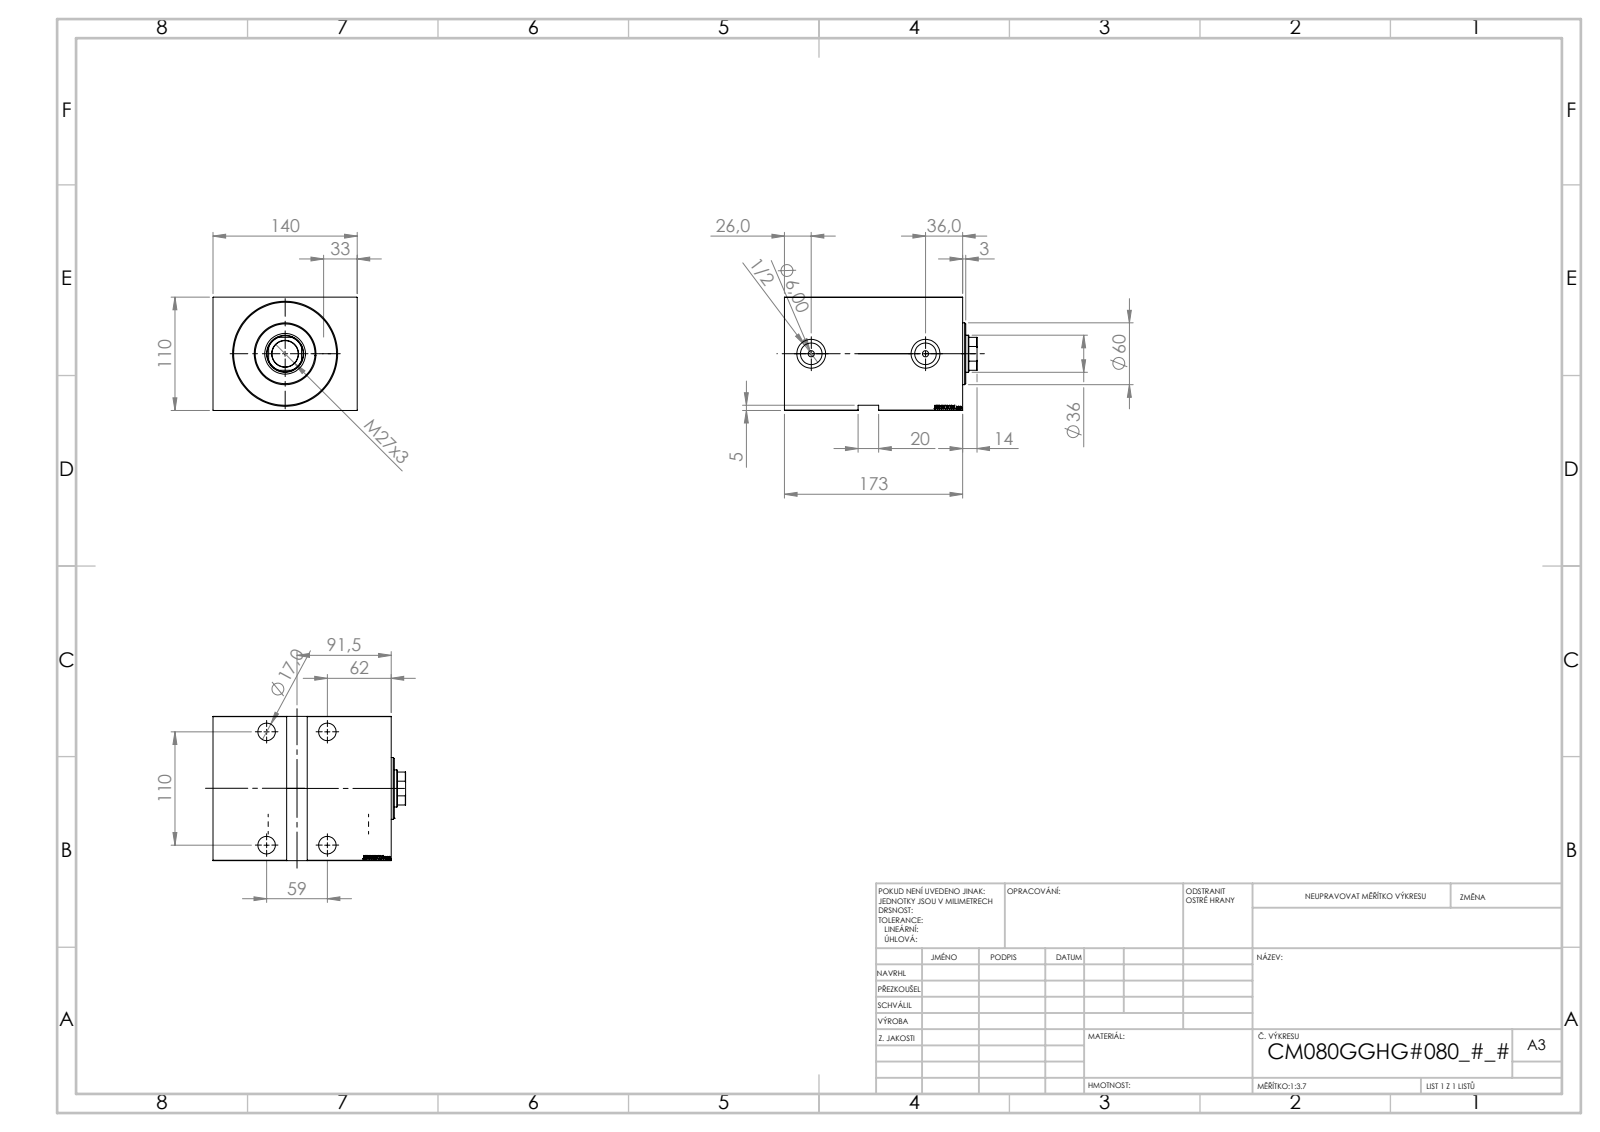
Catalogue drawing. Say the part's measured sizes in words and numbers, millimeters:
The part is named "V450CM_VC_G; V450CM_G_VCP; Zatka_OIL_PORT; V450CM_G_Body". Its 3-D file was written by "SolidWorks 2019 (CONFIG_CONTROL_DESIGN)". It is 5 solids with 894 faces: 440 planar, 56 cylindrical and 398 other. Overall it measures 187 by 140 by 110 millimeters. Its volume is 2 159 000 cubic millimeters and its surface area 242 546 square millimeters. Round holes: 4 of diameter 17, 4 of diameter 25, 2 of diameter 6, 2 of diameter 20.96, 2 of diameter 28, 1 of diameter 25.5, 1 of diameter 36, 1 of diameter 39.5, 1 of diameter 80, 1 of diameter 82, 1 of diameter 100. Round bosses or shafts: 2 of diameter 26, 1 of diameter 60. Partial cylindrical surfaces (rounded edges, fillets, slot ends): 1 of radius 17.5. The main face-to-face distances are 110, 140, 5, 173, 21, 152, 168, 147, 79, 58. The hole center spacings are 59, 110, 124.82, 111.
